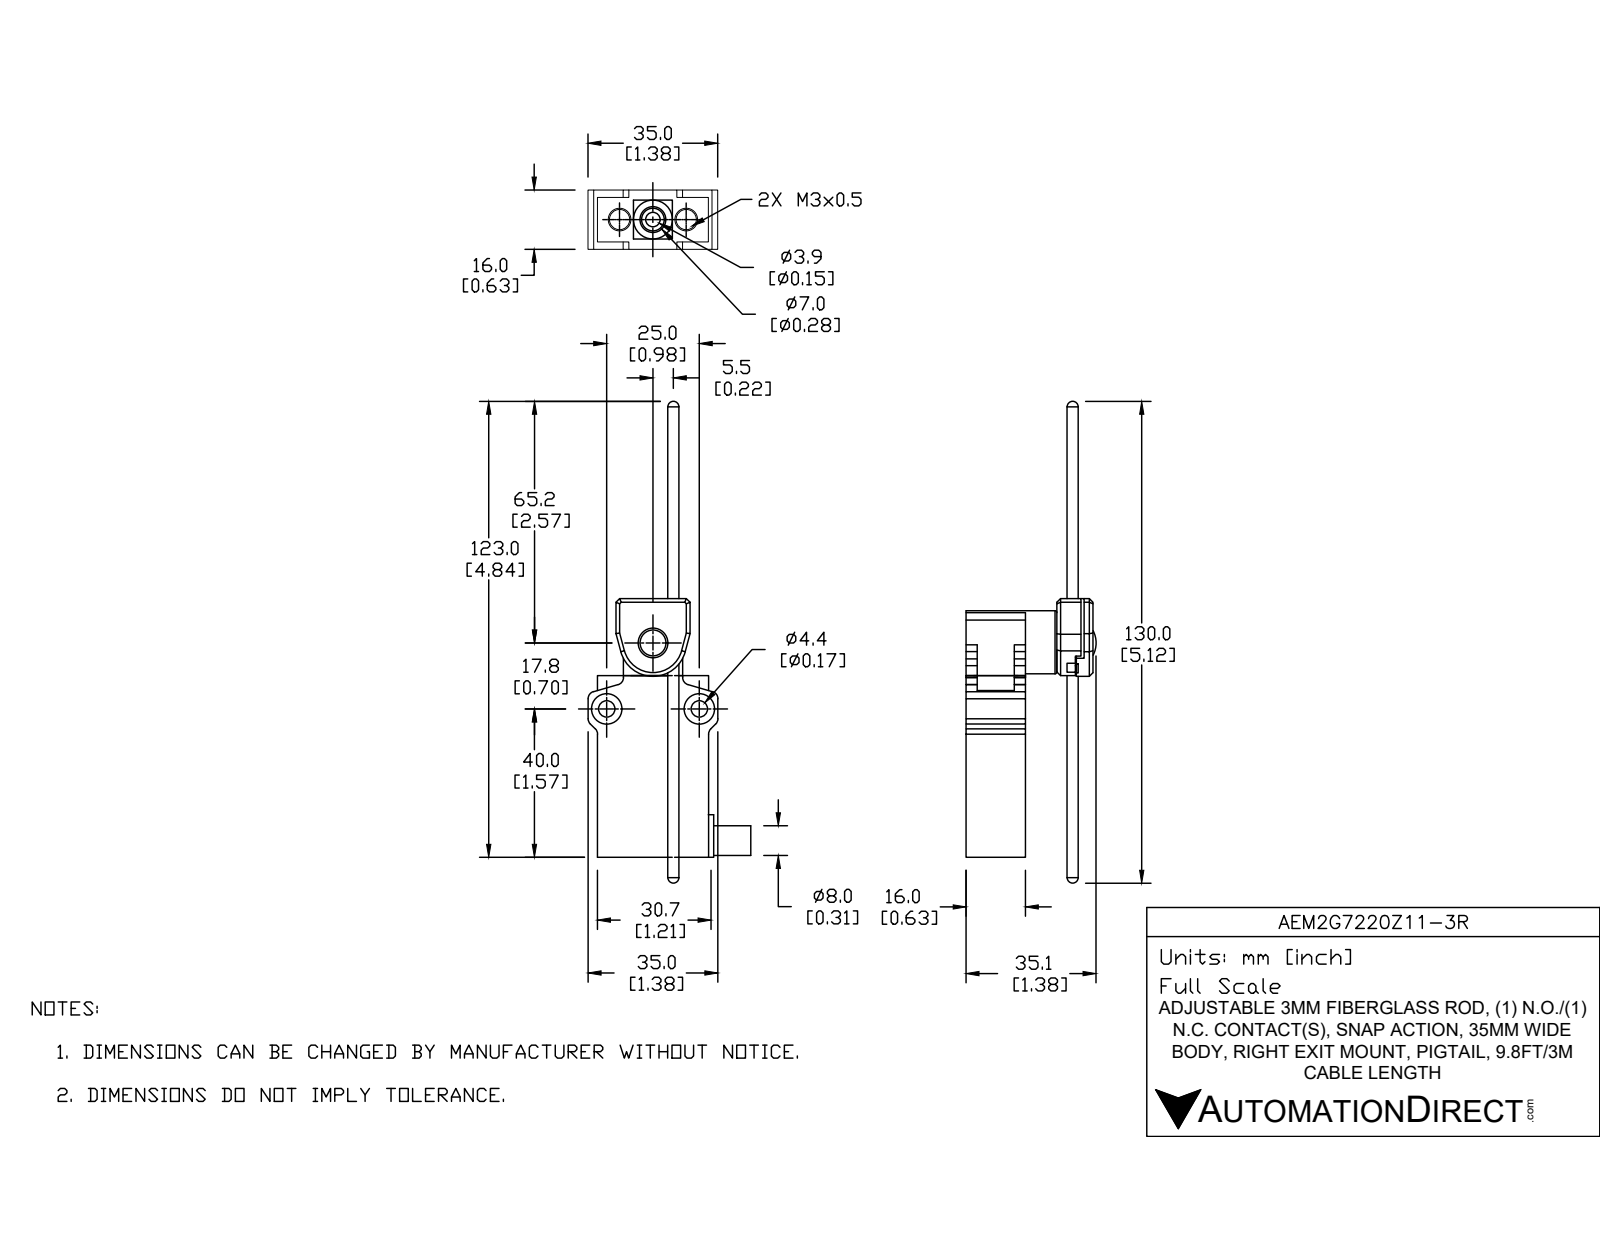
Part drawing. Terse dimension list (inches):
name: AEM2G7220Z11-3R
written by: SolidWorks 2017 (AUTOMOTIVE_DESIGN)
unit: in
bodies: 7 solids, 221 faces (139 planar, 65 cylindrical, 17 other)
size: 6.693 × 1.87 × 1.366
volume: 1.945 in³; area: 20.49 in²
holes: 2× ⌀0.118, 2× ⌀0.173, 2× ⌀0.323, 1× ⌀0.138, 1× ⌀0.197, 1× ⌀0.315
bosses: 1× ⌀0.622, 1× ⌀0.323, 1× ⌀0.276, 1× ⌀0.118
rounds: 8× R0.079, 1× R0.059, 1× R0.173, 1× R0.256, 1× R0.26, 1× R0.354
face distances: 0.63, 1.181, 1.929, 0.169, 0.472, 0.902, 0.28, 0.098, 0.697, 0.988
hole spacings: 0.863, 0.748, 0.984
